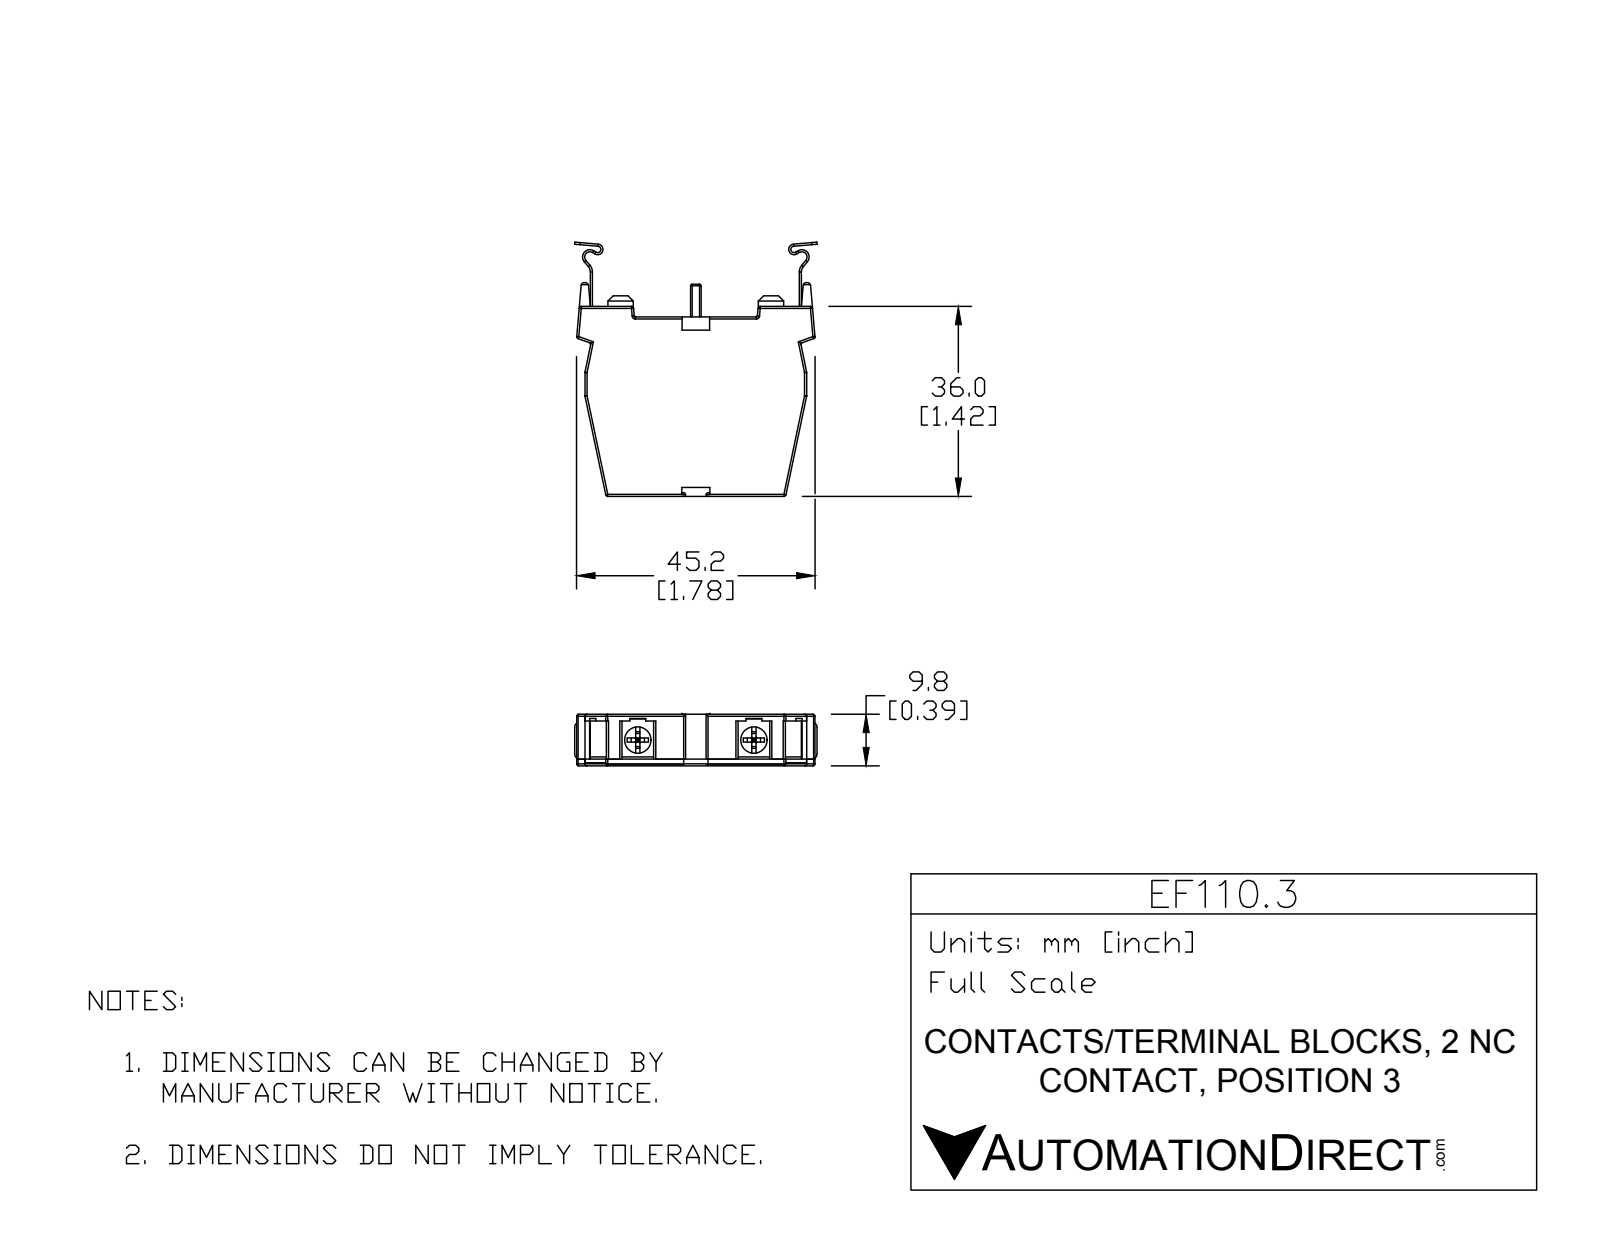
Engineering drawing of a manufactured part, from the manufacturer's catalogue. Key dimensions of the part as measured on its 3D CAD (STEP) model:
Part name (STEP PRODUCT): EF110.3
STEP written by: SolidWorks 2015 (AUTOMOTIVE_DESIGN)
Units: millimetres
Bodies: 7 solids, 299 faces (173 planar, 104 cylindrical, 22 other)
Overall size (bounding box): 48.16 × 46.28 × 9.8
Volume: 12 135 mm³ · Surface area: 6 604 mm²
Round holes (diameter × count): ⌀5 ×4
Round bosses / shafts (diameter × count): ⌀4 ×4, ⌀4.75 ×2
Partial cylindrical surfaces — rounded edges, fillets, slot ends (radius × count): R0.25 ×44, R0.5 ×8, R1 ×6, R0.6 ×4, R0.6 ×2, R1 ×2, R1.4 ×2, R1.6 ×2
Main face-to-face distances: 9.8, 1.4, 8.4, 34, 7, 2, 0.4, 3.18, 37.18, 36
Hole centre spacings: 21.81
